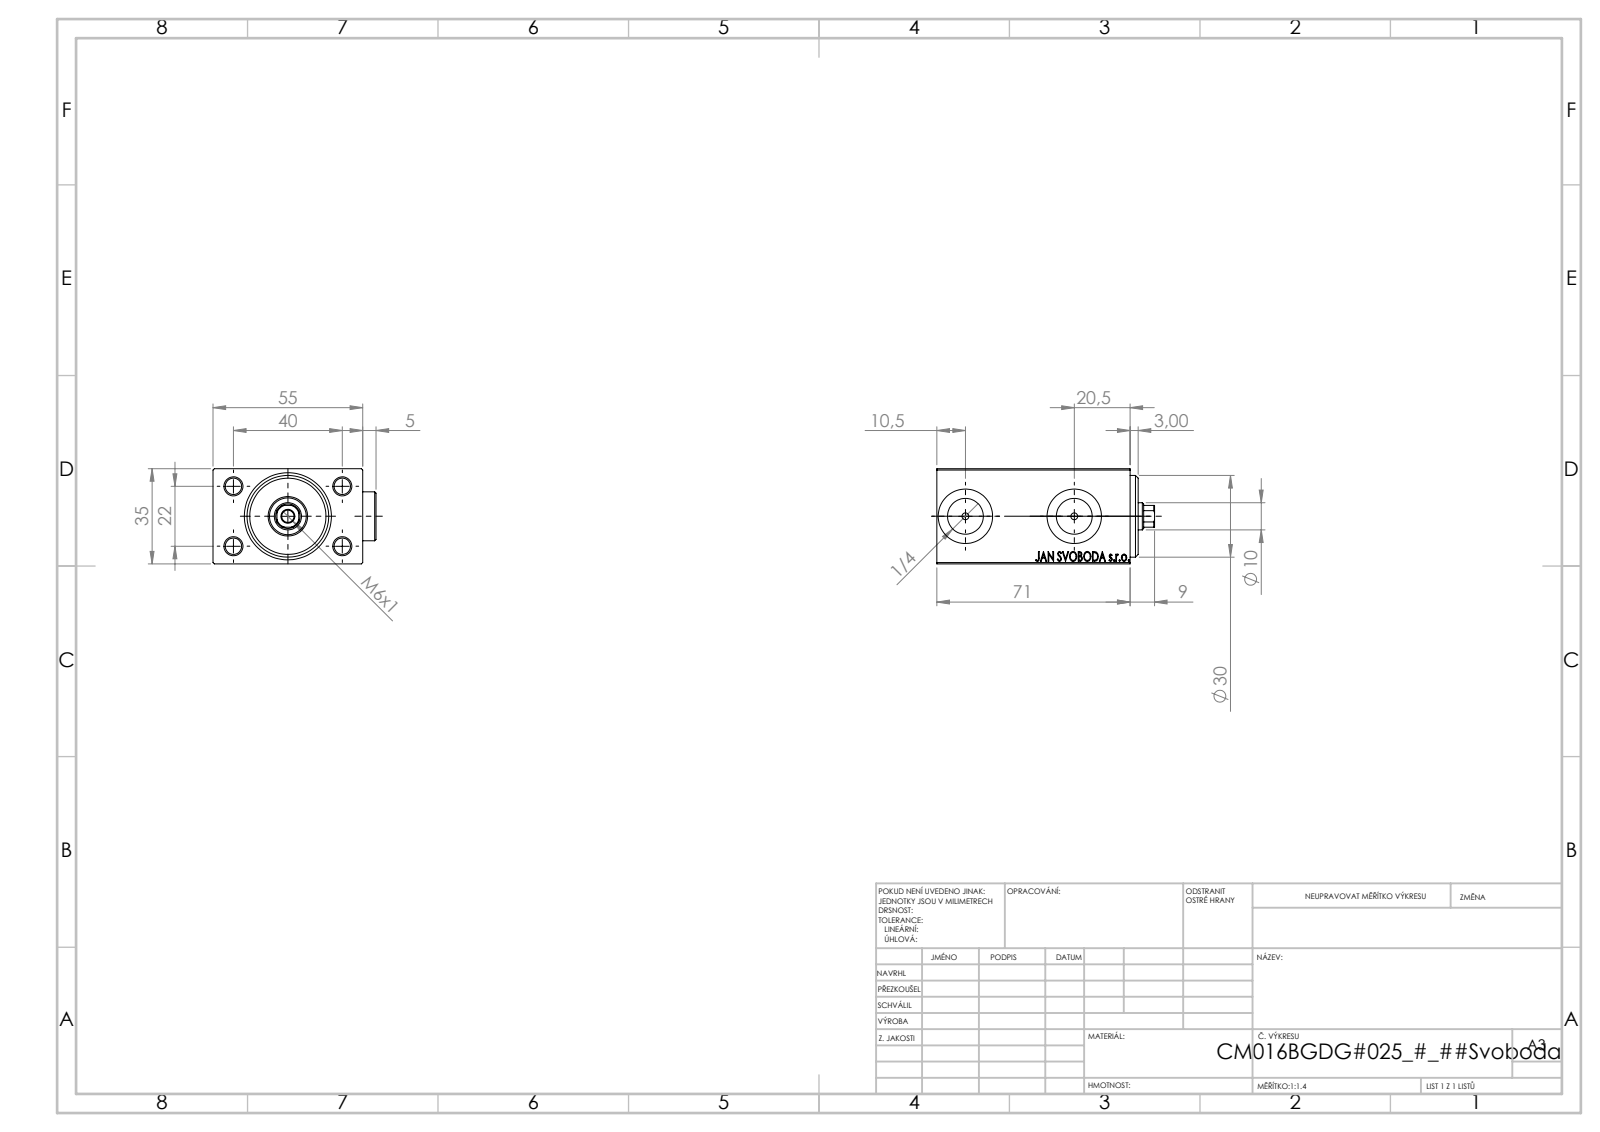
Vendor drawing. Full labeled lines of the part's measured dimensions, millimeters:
Part name (STEP PRODUCT): V450CM_B_Body; V450CM_B_VCP; Zatka_OIL_PORT; V450CM_VC_B
STEP written by: SolidWorks 2019 (CONFIG_CONTROL_DESIGN)
Units: millimetres
Bodies: 5 solids, 935 faces (435 planar, 70 cylindrical, 430 other)
Overall size (bounding box): 80 × 59.9 × 35
Volume: 128 255 mm³ · Surface area: 31 780 mm²
Round holes (diameter × count): ⌀6 ×4, ⌀2.5 ×2, ⌀13.16 ×2, ⌀20 ×2, ⌀4.5 ×1, ⌀10 ×1, ⌀13.5 ×1, ⌀14.5 ×1, ⌀16 ×1, ⌀18 ×1, ⌀30 ×1
Round bosses / shafts (diameter × count): ⌀18 ×2
Partial cylindrical surfaces — rounded edges, fillets, slot ends (radius × count): R4.5 ×1
Main face-to-face distances: 35, 55, 5, 66, 54.9, 71, 3, 8, 74, 54.8
Hole centre spacings: 22.83, 40, 22, 45.65
